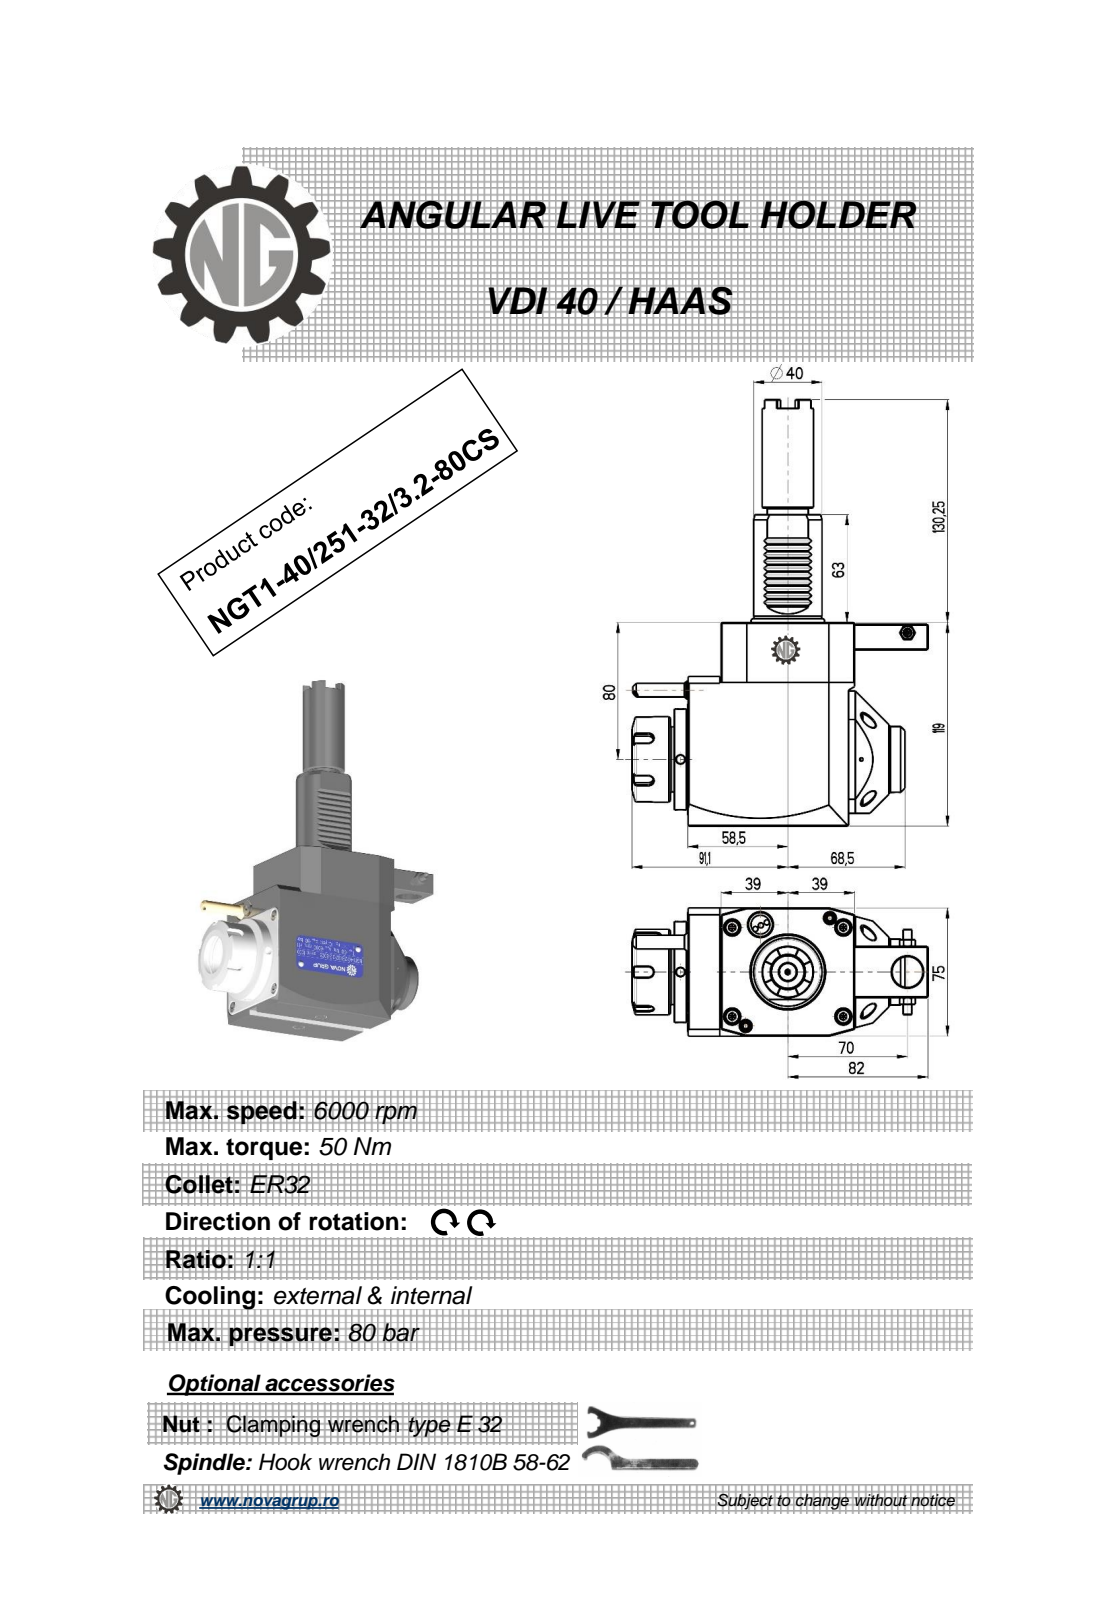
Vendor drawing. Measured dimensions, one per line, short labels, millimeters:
name: NGT1_40_251_32_3_2_80CS
written by: PRO/ENGINEER BY PARAMETRIC TECHNOLOGY CORPORATION, 2010280 (CONFIG_CONTROL_DESIGN)
unit: mm
bodies: 1 solid, 490 faces (243 planar, 97 cylindrical, 150 other)
size: 249.25 × 173.1 × 75
volume: 1 066 000 mm³; area: 89 174 mm²
holes: 3× ⌀5, 1× ⌀3, 1× ⌀4.2, 1× ⌀9.5, 1× ⌀18, 1× ⌀20, 1× ⌀27, 1× ⌀46
bosses: 1× ⌀59, 1× ⌀50, 1× ⌀46, 1× ⌀41, 1× ⌀40, 1× ⌀38.5, 1× ⌀30, 1× ⌀24
rounds: 12× R0.26, 10× R0.3, 6× R0.2, 5× R3, 2× R5.8, 2× R6, 2× R600, 1× R0.5
face distances: 75, 119, 19.5, 97.5, 78, 19.3, 97.3, 27.5, 1, 3.5
hole spacings: 36.47, 44.12, 62.75, 70, 72.5, 132.75, 151.98
